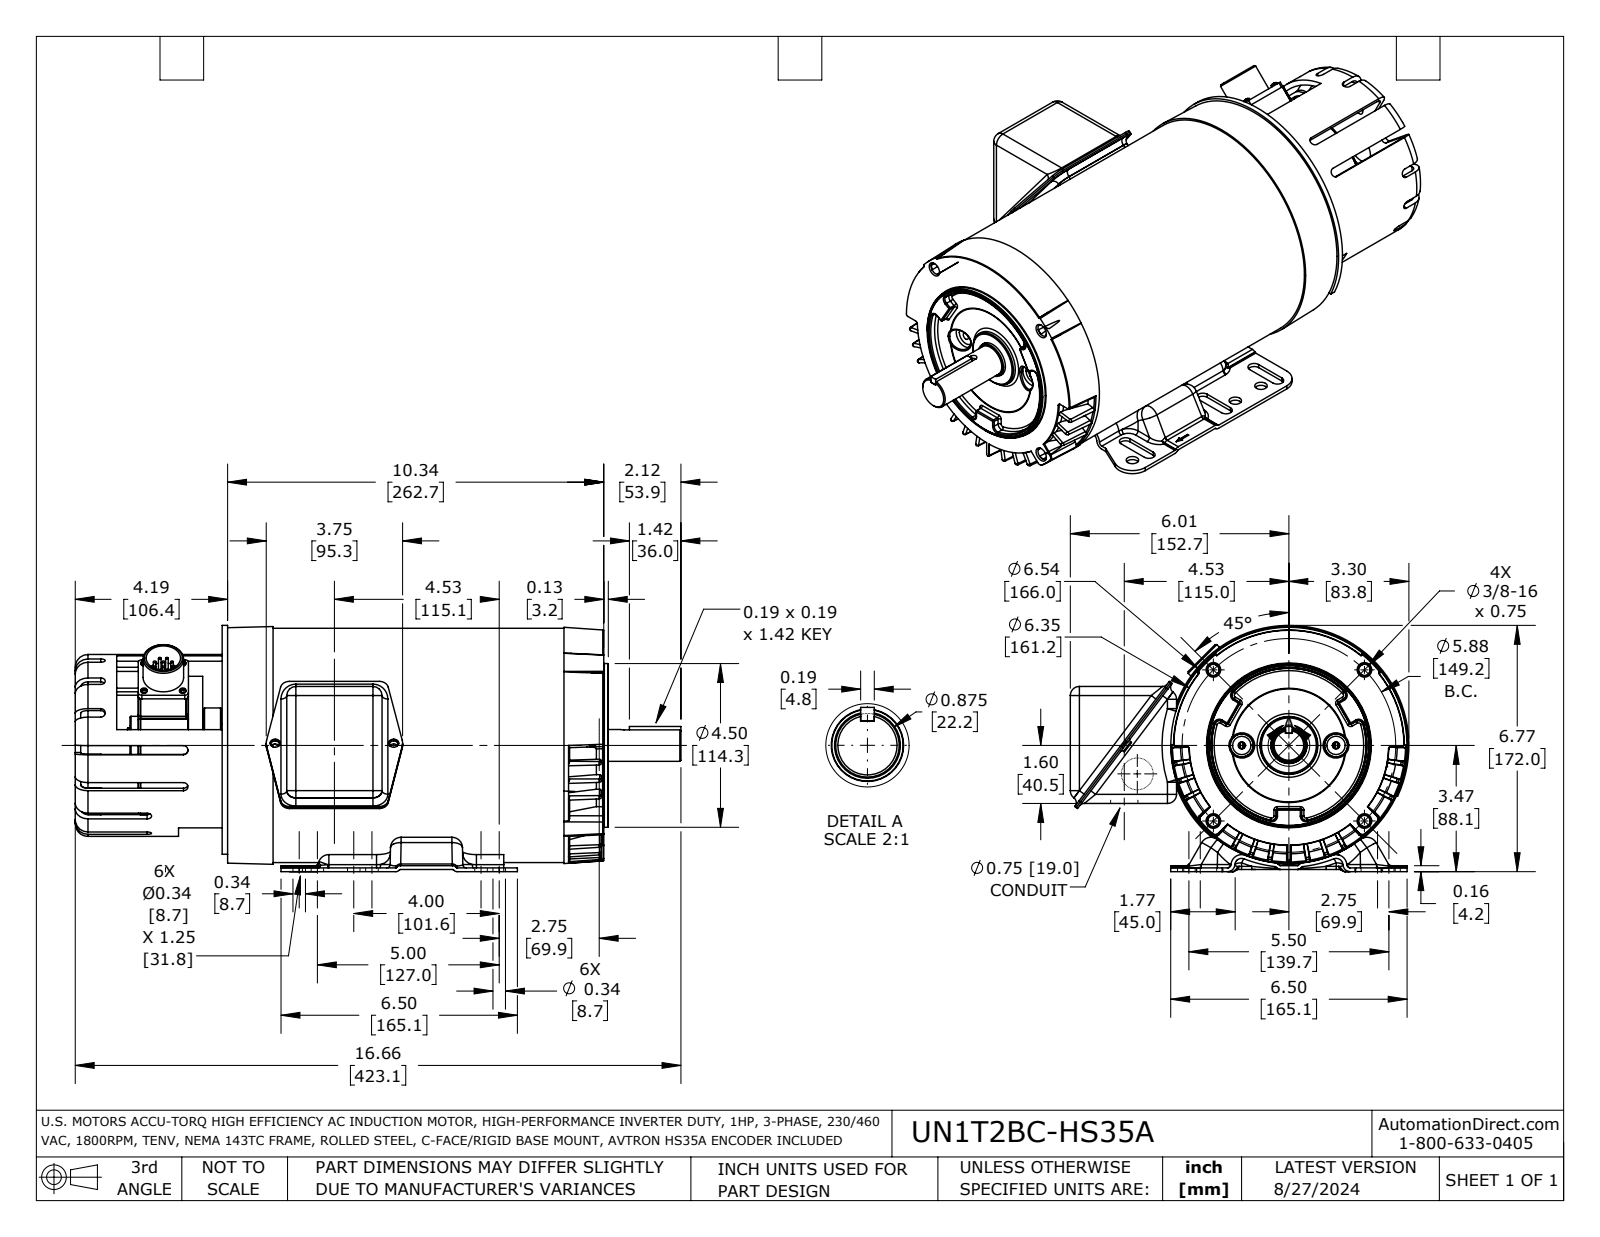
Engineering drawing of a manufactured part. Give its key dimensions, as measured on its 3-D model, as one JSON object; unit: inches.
{"part_name": "UN1T2BC-HS35A", "step_written_by": "SolidWorks 2021 (AUTOMOTIVE_DESIGN)", "units": "inches", "bodies": {"solids": 26, "faces": 3056, "planar": 755, "cylindrical": 719, "other": 1582}, "overall_size": [16.656, 9.311, 6.77], "volume_in3": 103.1, "surface_area_in2": 1168, "round_holes": [[0.25, 8], [0.344, 6], [0.4, 6], [0.12, 4], [0.2, 4], [0.302, 4], [0.421, 4], [0.55, 4], [0.136, 3], [0.098, 2], [0.173, 2], [0.229, 2]], "round_bosses_or_shafts": [[0.072, 8], [0.175, 4], [0.12, 4], [0.15, 3], [0.325, 2], [0.072, 2], [6.44, 1], [6.315, 1]], "partial_cylinders_radius": [[0.062, 91], [0.031, 71], [0.125, 42], [0.25, 26], [0.202, 18], [0.094, 14], [0.048, 12], [0.172, 12]], "face_to_face_distances": [0.048, 1.08, 1.375, 2.455, 0.15, 4.04, 0.104, 0.12, 0.53, 0.06], "hole_center_spacings": [2.098, 2.246, 3.419, 4.349, 5.422, 2.073, 2.232, 2.234]}
